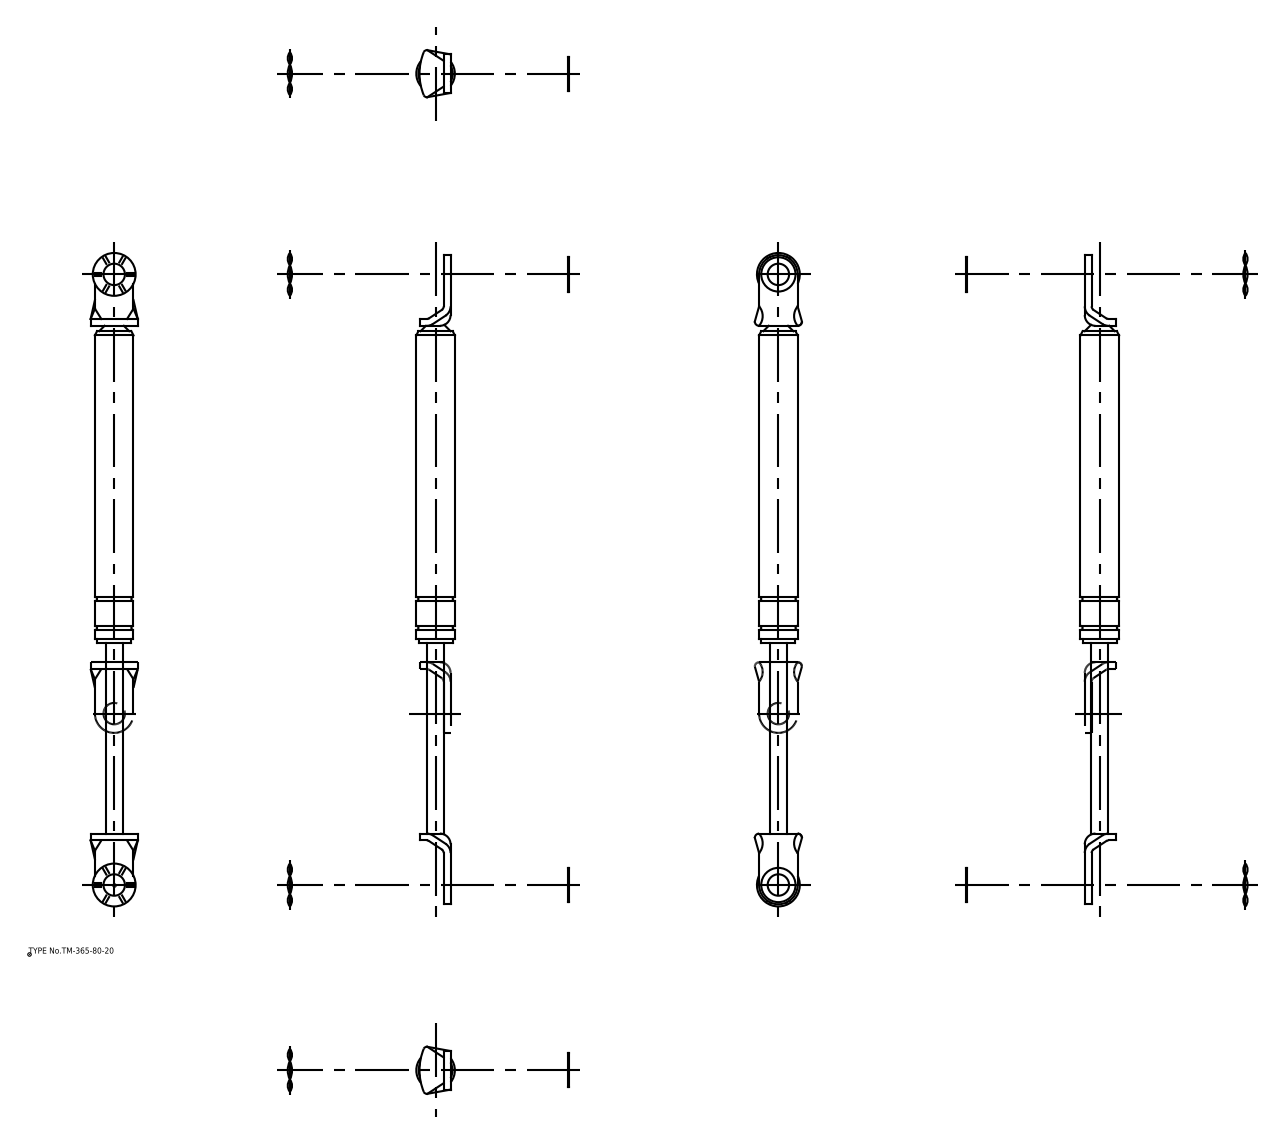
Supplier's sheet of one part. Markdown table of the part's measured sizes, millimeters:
| quantity | value |
| --- | --- |
| part name | ウェーブワッシャー; ワッシャー; 本体; 本体_div |
| STEP written by | spGate 16.7.1 (AUTOMOTIVE_DESIGN) |
| units | millimeters |
| bodies | 6 solids, 94 faces (42 planar, 44 cylindrical, 8 other) |
| overall size | 305 × 22 × 18.5 |
| volume | 47 111 mm³ |
| surface area | 16 619 mm² |
| round holes (diameter × count) | 10 × 2 |
| round bosses / shafts (diameter × count) | 16 × 3, 20 × 2, 18.5 × 1, 18 × 1, 8 × 1 |
| partial cylindrical surfaces (radius × count) | 4.4 × 2, 5 × 2, 9 × 2, 26.32 × 1 |
| main face-to-face distances | 3.2, 2, 5.2, 240.2, 3.7, 5.7, 0.5, 151.2, 92.2, 243.4 |
| hole center spacings | 285 |
